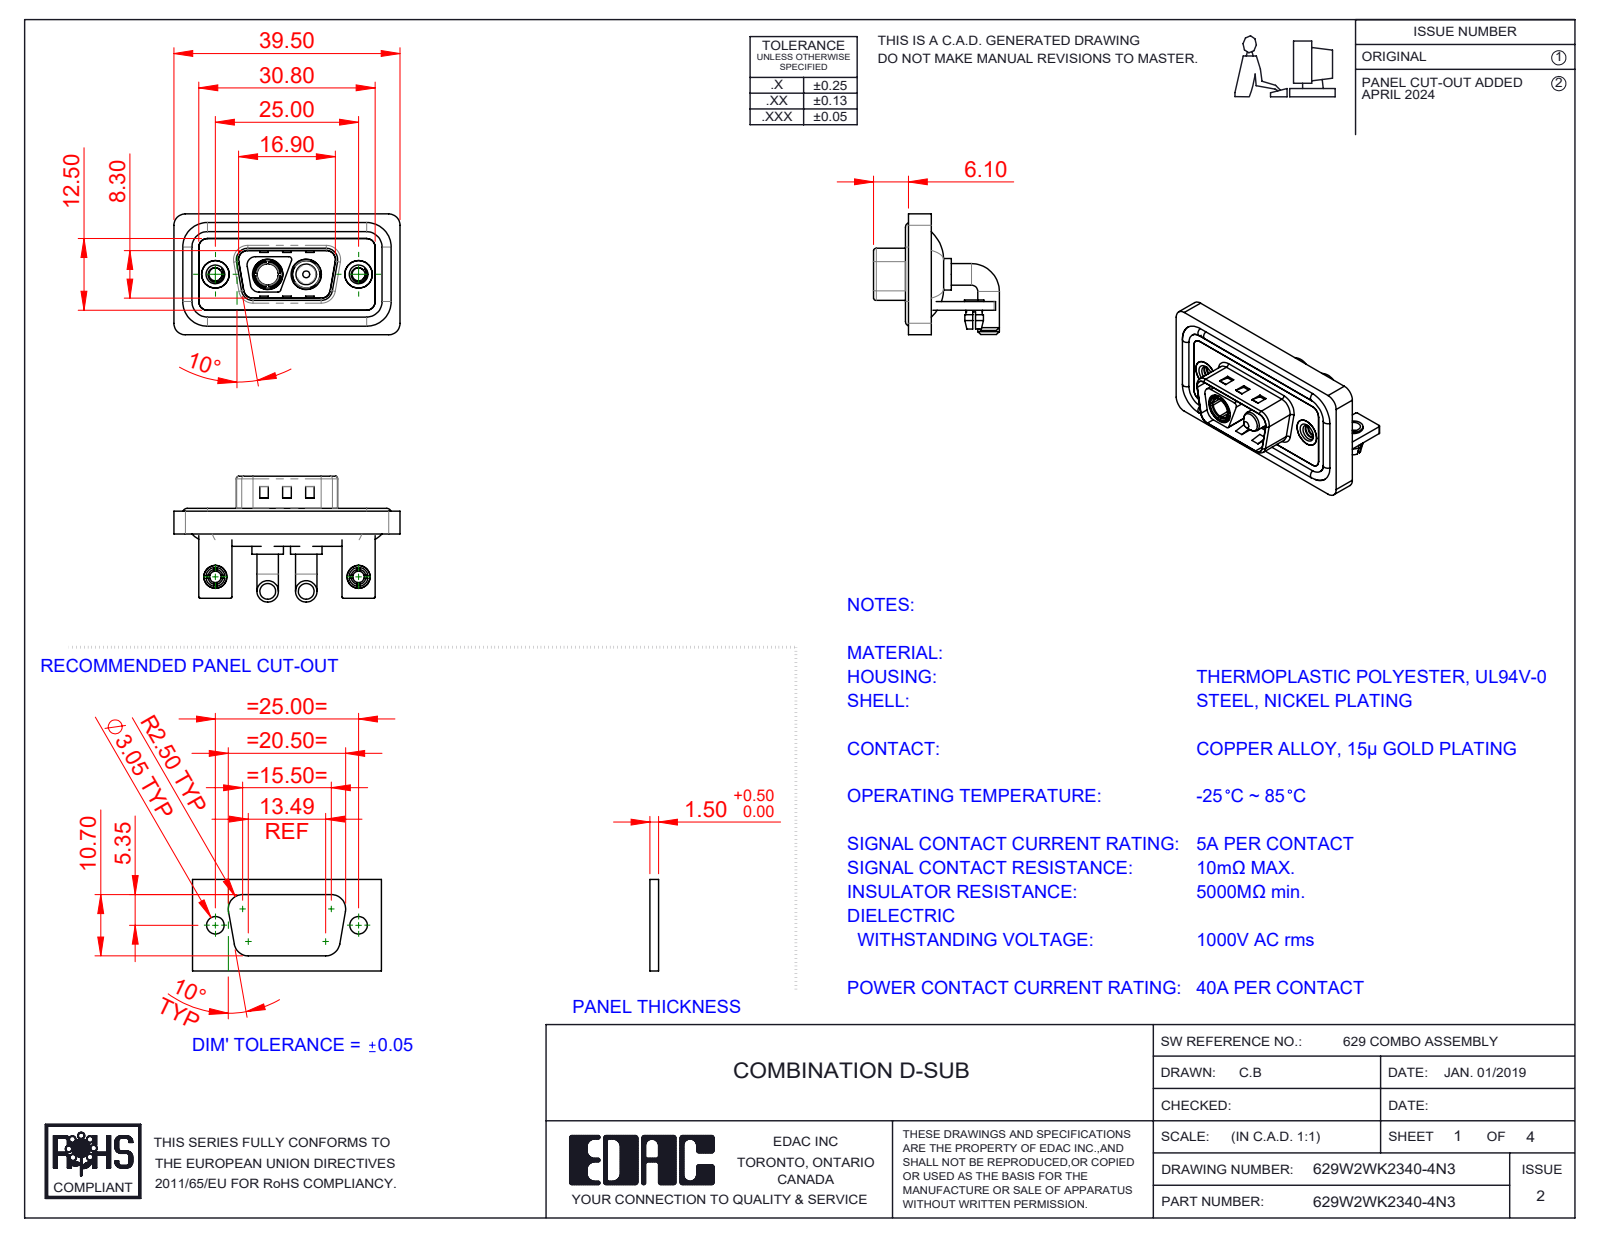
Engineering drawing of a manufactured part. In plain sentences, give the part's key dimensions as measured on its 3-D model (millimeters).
The part is named "629Combo Waterproof Housing_09 Contacts; 629Combo Board Lock; 629W2WK2340-4N3; 629Combo Shell Rear_09 Contacts (+6 more)". Its 3-D file was written by "SolidWorks 2023 (CONFIG_CONTROL_DESIGN)". It is 15 solids with 674 faces: 257 planar, 281 cylindrical and 136 other. Overall it measures 39.5 by 21.98 by 21.1 millimeters. Its volume is 5 145 cubic millimeters and its surface area 8 419 square millimeters. Round holes: 2 of diameter 2, 2 of diameter 2.26, 2 of diameter 2.5, 2 of diameter 3.2, 2 of diameter 4, 2 of diameter 4.8, 2 of diameter 4.85, 2 of diameter 5, 2 of diameter 5.3, 1 of diameter 3.7. Round bosses or shafts: 4 of diameter 3.75, 4 of diameter 1.6, 2 of diameter 5.5, 2 of diameter 5.2, 2 of diameter 4.9, 2 of diameter 4.75, 2 of diameter 4, 2 of diameter 3.4. Partial cylindrical surfaces (rounded edges, fillets, slot ends): 20 of radius 1.5, 19 of radius 2, 16 of radius 0.25, 11 of radius 0.5, 8 of radius 1.6, 4 of radius 0.6, 4 of radius 0.65, 4 of radius 0.9. The main face-to-face distances are 0.4, 1.5, 2.9, 0.8, 1.1, 1.2, 2.1, 1.6, 3.7, 2.5. The hole center spacings are 9.14, 15.86, 25, 6.72.
